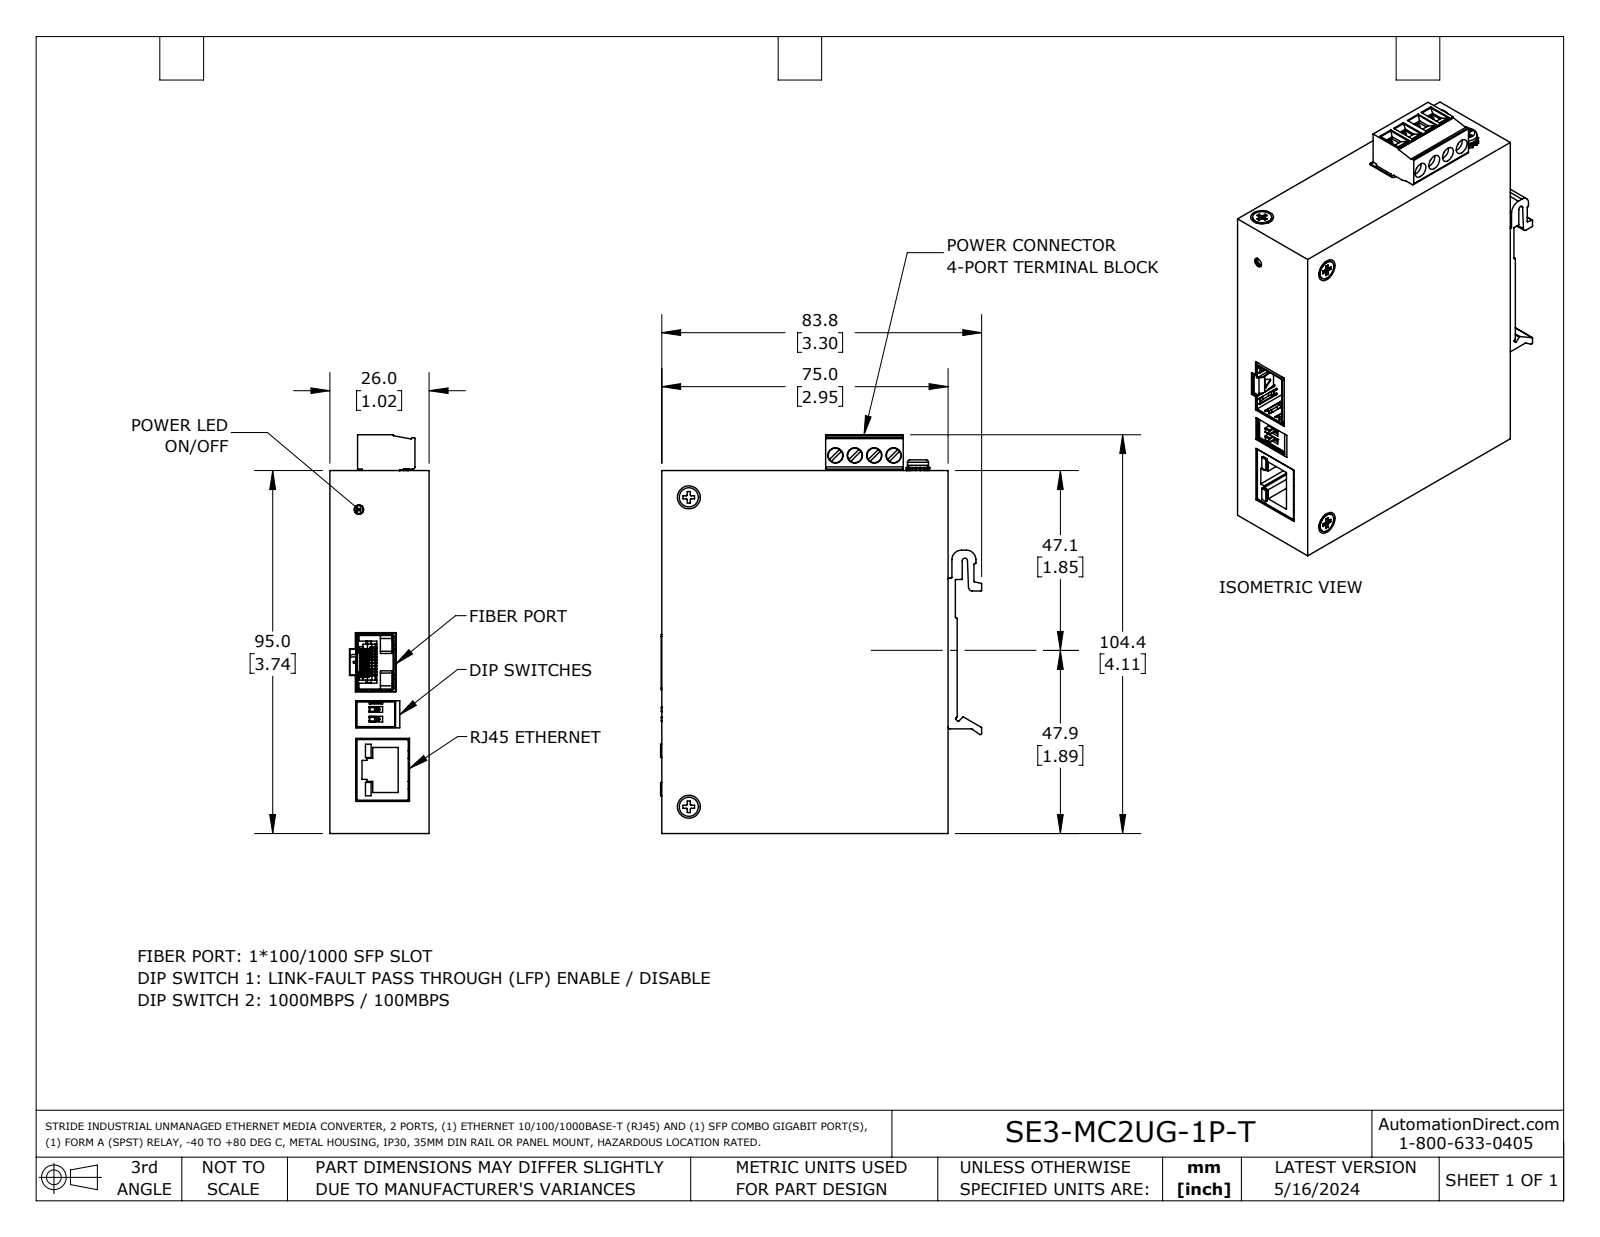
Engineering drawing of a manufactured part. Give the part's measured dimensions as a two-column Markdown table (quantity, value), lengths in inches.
| quantity | value |
| --- | --- |
| part name | SE3-MC2UG-1P-T |
| STEP written by | SolidWorks 2023 (AUTOMOTIVE_DESIGN) |
| units | inches |
| bodies | 23 solids, 3243 faces (2199 planar, 872 cylindrical, 172 other) |
| overall size | 4.11 × 3.311 × 1.024 |
| volume | 1.977 in³ |
| surface area | 98.25 in² |
| round holes (diameter × count) | 0.079 × 12, 0.157 × 7, 0.055 × 4, 0.11 × 4, 0.118 × 4, 0.059 × 1, 0.091 × 1, 0.098 × 1 |
| round bosses / shafts (diameter × count) | 0.197 × 9, 0.118 × 9, 0.149 × 4, 0.217 × 1, 0.114 × 1 |
| partial cylindrical surfaces (radius × count) | 0.008 × 105, 0.01 × 81, 0.004 × 68, 0.02 × 50, 0.006 × 44, 0.008 × 18, 0.079 × 18, 0.011 × 9 |
| main face-to-face distances | 0.039, 0.984, 0.02, 0.945, 1.024, 2.913, 1.004, 0.965, 3.701, 2.953 |
| hole center spacings | 0.237, 0.554, 0.354, 0.2, 0.474, 0.709, 0.9, 0.315 |
